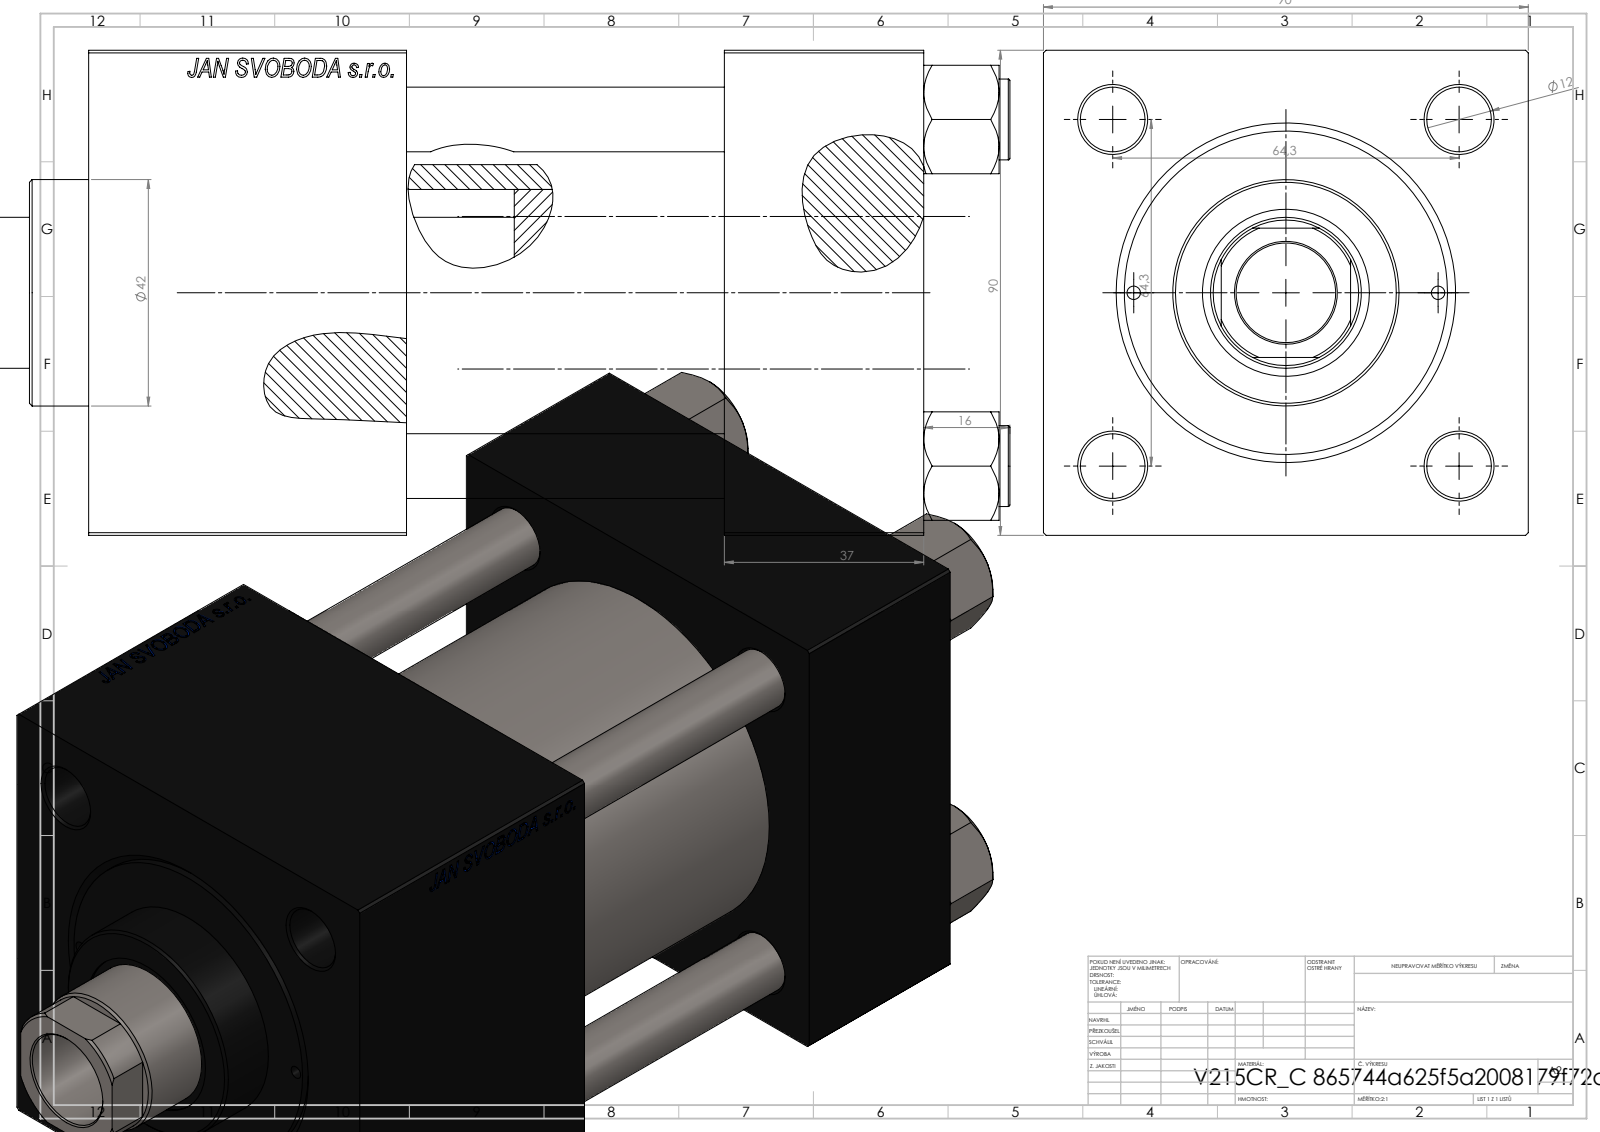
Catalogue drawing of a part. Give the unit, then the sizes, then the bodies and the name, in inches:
Units: inches
Overall size (bounding box): 7.992 × 3.543 × 3.543
Round holes (diameter × count): ⌀0.472 ×4, ⌀0.098 ×2, ⌀0.276 ×2, ⌀0.825 ×2, ⌀1.181 ×2, ⌀0.728 ×1, ⌀1.102 ×1, ⌀1.22 ×1, ⌀1.969 ×1, ⌀2.362 ×1, ⌀2.48 ×1
Round bosses / shafts (diameter × count): ⌀0.591 ×4, ⌀2.717 ×1, ⌀1.654 ×1
Partial cylindrical surfaces — rounded edges, fillets, slot ends (radius × count): R0.531 ×1
Main face-to-face distances: 3.543, 2.323, 1.457, 6.102, 4.646, 3.78, 4.972, 3.516, 1.193, 1.13
Hole centre spacings: 1.275, 1.79, 2.531, 2.694, 1.112, 3.58, 2.224, 3.839
Volume: 57.78 in³ · Surface area: 277.8 in²
Bodies: 11 solids, 1154 faces (528 planar, 90 cylindrical, 536 other)
Part name (STEP PRODUCT): V215CR_C_TYCINKA; V215CR_VCP_C; V215_VC_A; V215CR_C_Body (+1 more)
STEP written by: SolidWorks 2019 (CONFIG_CONTROL_DESIGN)
